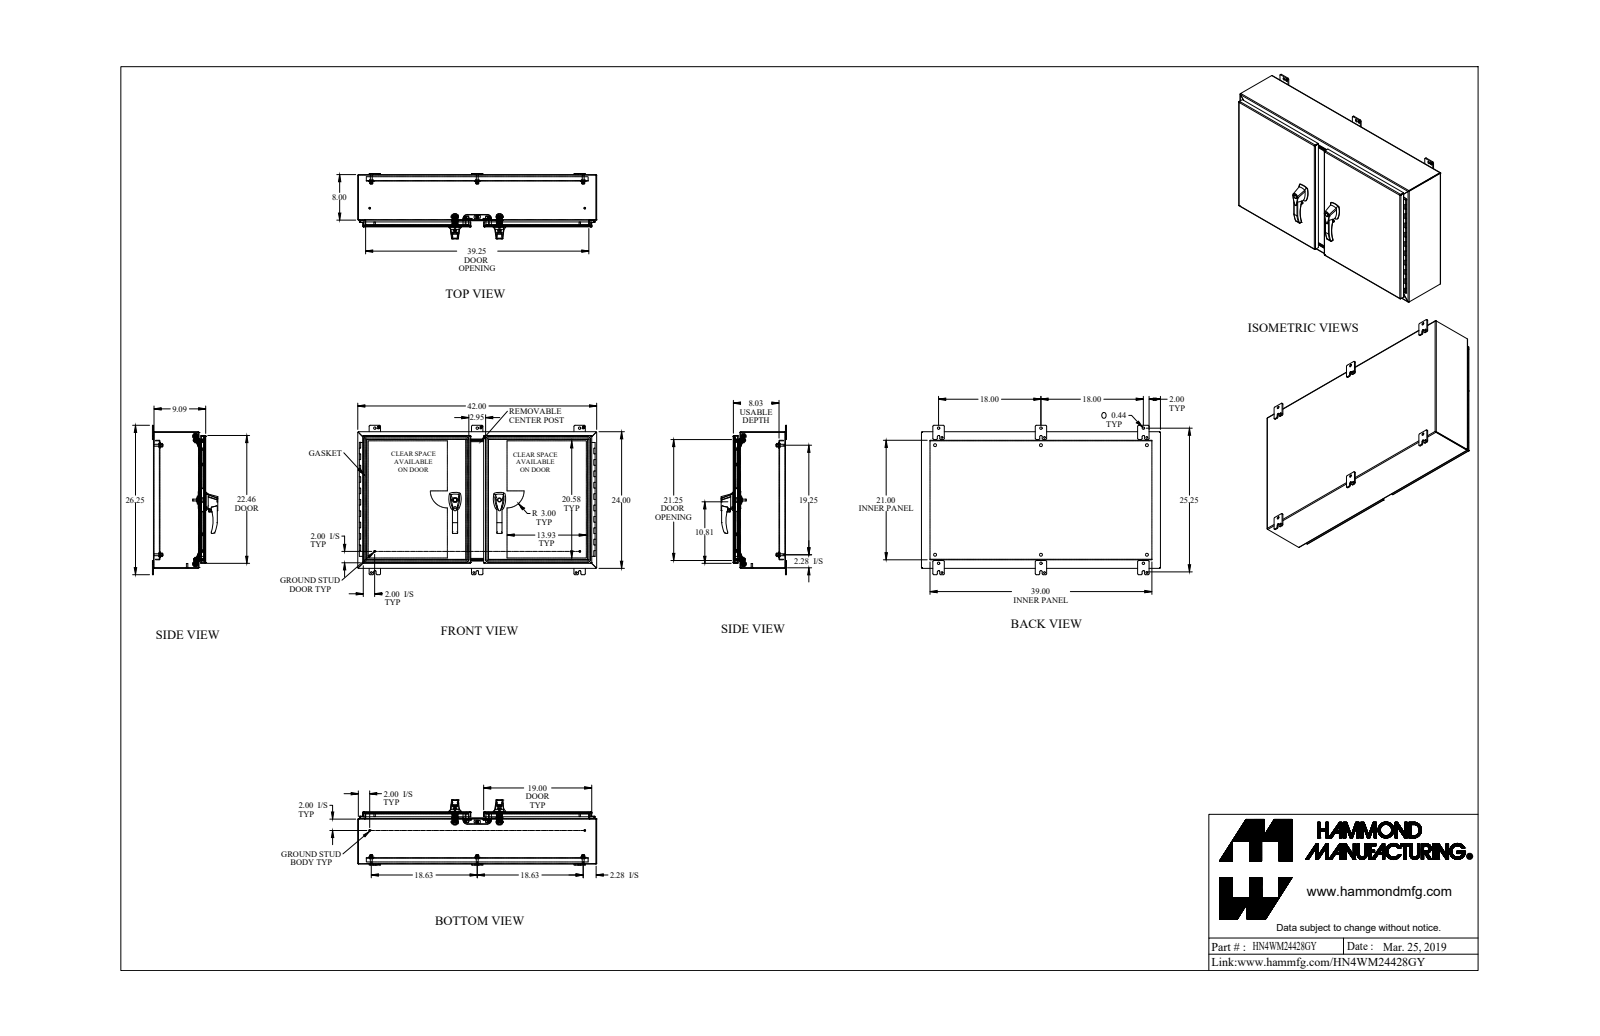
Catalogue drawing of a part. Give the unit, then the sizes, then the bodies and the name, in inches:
Units: inches
Overall size (bounding box): 42 × 26.25 × 11.487
Round holes (diameter × count): ⌀0.25 ×10, ⌀0.313 ×9, ⌀0.304 ×8, ⌀0.201 ×6, ⌀0.307 ×6, ⌀0.445 ×6, ⌀0.5 ×6, ⌀0.257 ×4, ⌀0.28 ×4, ⌀0.281 ×4, ⌀0.313 ×4, ⌀0.39 ×4
Round bosses / shafts (diameter × count): ⌀1 ×10, ⌀0.281 ×8, ⌀0.65 ×6, ⌀0.375 ×6, ⌀0.33 ×6, ⌀0.293 ×6, ⌀0.75 ×4, ⌀0.63 ×4
Partial cylindrical surfaces — rounded edges, fillets, slot ends (radius × count): R0.125 ×37, R0.018 ×32, R0.188 ×27, R0.25 ×26, R0.06 ×22, R0.5 ×21, R0.048 ×19, R0.143 ×19
Main face-to-face distances: 0.095, 1.032, 0.095, 9.09, 8.995, 0.937, 9.185, 9.09, 1.127, 7.963
Hole centre spacings: 7.814, 6, 40.588, 1.126, 1.287, 2.041, 7.276, 7.895
Volume: 483.2 in³ · Surface area: 9 870 in²
Bodies: 108 solids, 2636 faces (1243 planar, 1101 cylindrical, 292 other)
Part name (STEP PRODUCT): HN4WM24428GY
STEP written by: SolidWorks 2018 (AUTOMOTIVE_DESIGN)
